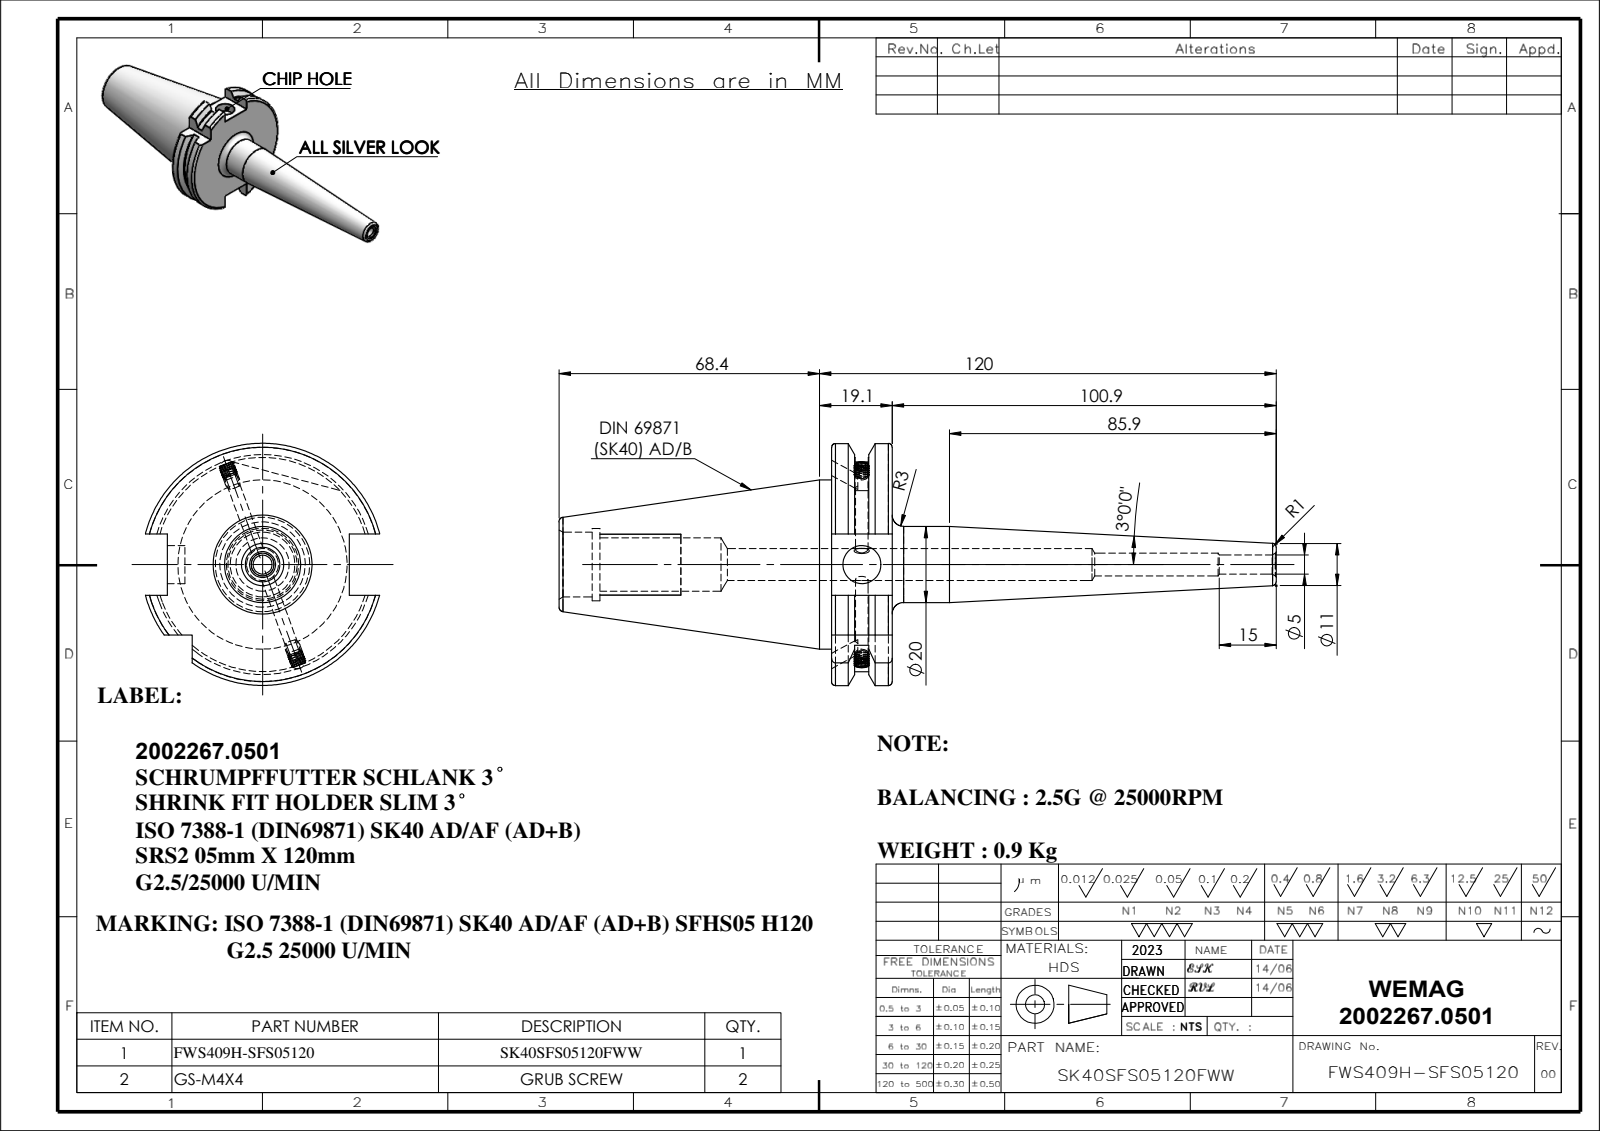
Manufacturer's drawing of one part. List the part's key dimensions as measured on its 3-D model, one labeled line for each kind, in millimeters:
Part name (STEP PRODUCT): SK40SFS05120FWW; 91406-SRS05120; GS-M4X4_DIN 913 - M4 x 4-N
STEP written by: SolidWorks 2018 (CONFIG_CONTROL_DESIGN)
Units: millimetres
Bodies: 3 solids, 198 faces (46 planar, 54 cylindrical, 98 other)
Overall size (bounding box): 188.4 × 63.55 × 61.48
Volume: 120 021 mm³ · Surface area: 28 017 mm²
Round holes (diameter × count): ⌀3.3 ×1, ⌀5 ×1, ⌀6 ×1, ⌀8.4 ×1, ⌀10 ×1, ⌀14 ×1, ⌀17 ×1, ⌀19 ×1
Round bosses / shafts (diameter × count): ⌀4 ×2, ⌀44.45 ×1, ⌀20 ×1
Partial cylindrical surfaces — rounded edges, fillets, slot ends (radius × count): R28.12 ×1, R31.77 ×1
Main face-to-face distances: 15.9, 16.1, 47.8, 71.6, 87.5, 10.7, 60.9, 76.8, 77.63, 66.93
